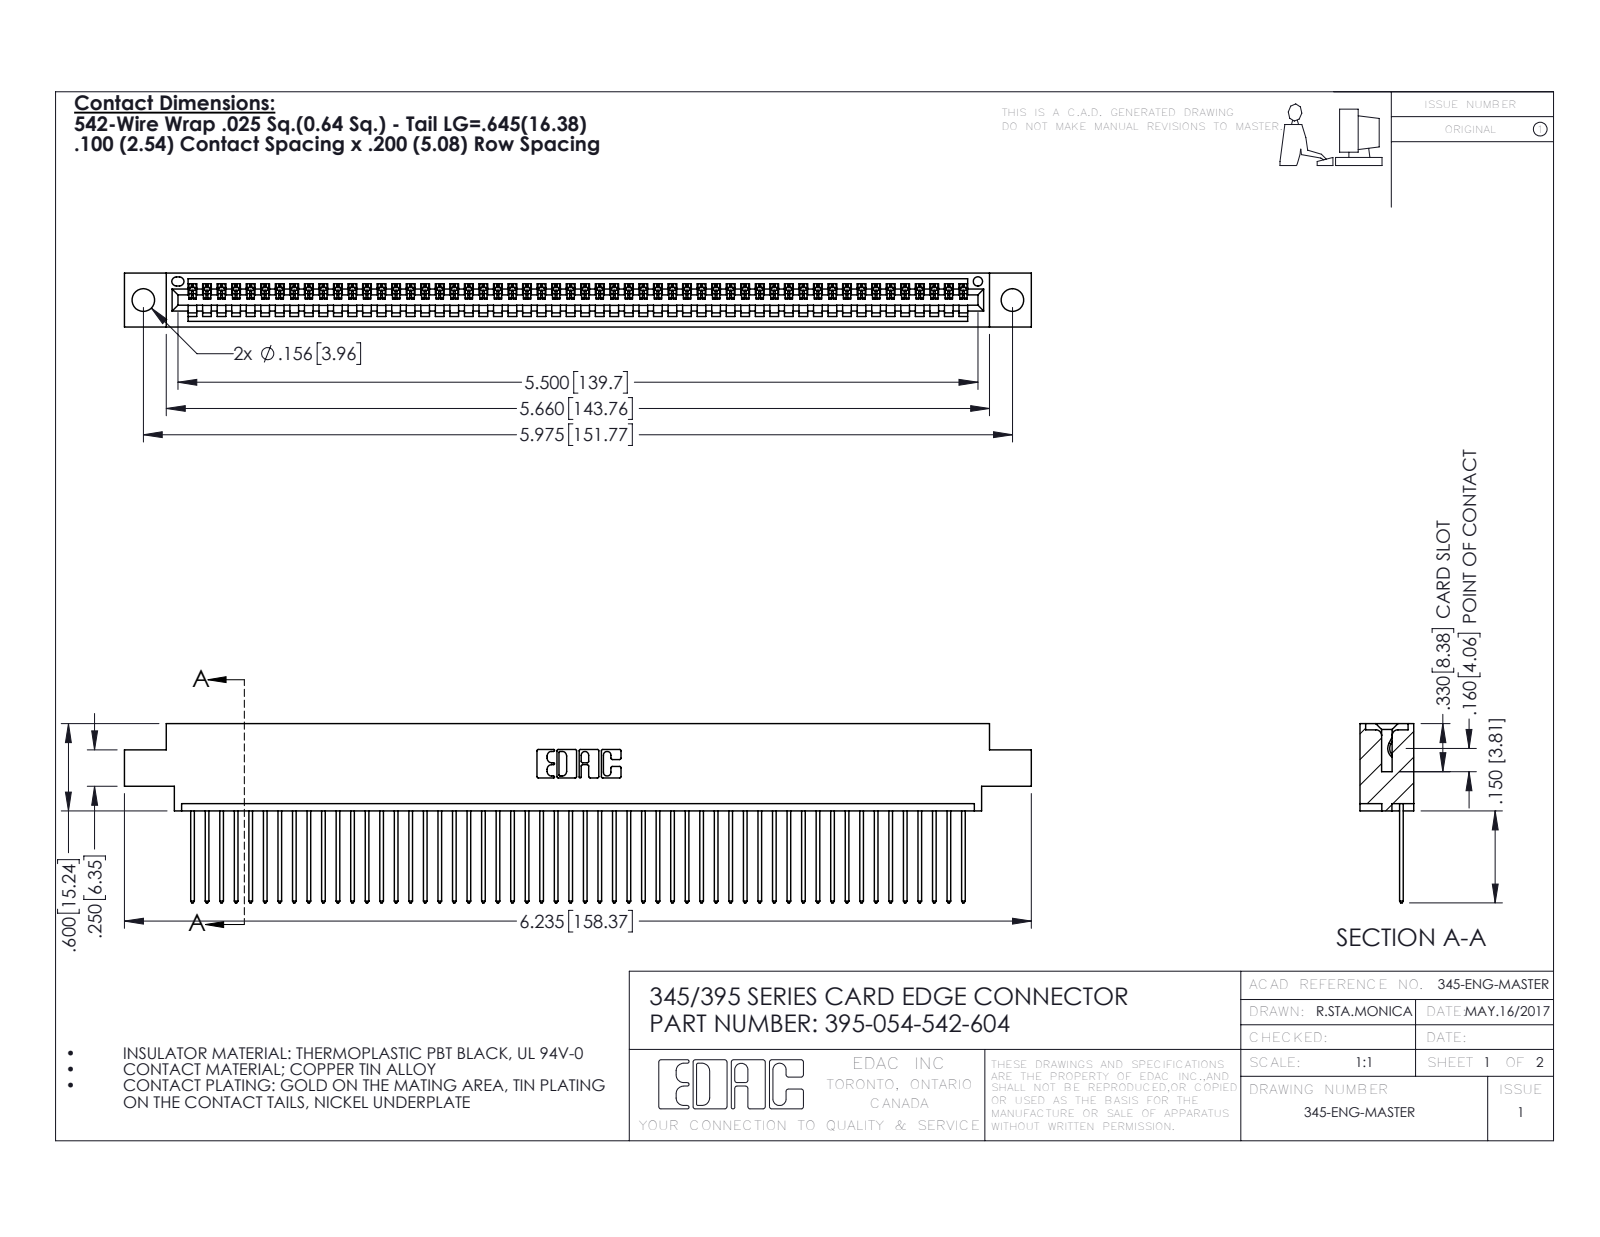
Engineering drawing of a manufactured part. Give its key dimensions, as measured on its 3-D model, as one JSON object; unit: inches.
{"part_name": "395-054-542-604; 345-292-001_345-293-142; 345 Part_0.170 Offset - 0.156 Dia-TH", "step_written_by": "SolidWorks 2016 (CONFIG_CONTROL_DESIGN)", "units": "inches", "bodies": {"solids": 55, "faces": 3262, "planar": 2244, "cylindrical": 1018, "other": 0}, "overall_size": [6.235, 1.232, 0.37], "volume_in3": 0.919, "surface_area_in2": 32.35, "round_holes": [[0.156, 2], [0.064, 1]], "partial_cylinders_radius": [[0.006, 108], [0.01, 108], [0.01, 22], [0.007, 6], [0.031, 6], [0.026, 3], [0.031, 2], [0.04, 2]], "face_to_face_distances": [0.072, 0.298, 0.37, 0.098, 0.272, 0.025, 0.2, 0.225, 0.175, 0.149], "hole_center_spacings": [0.27, 5.739, 5.975]}
